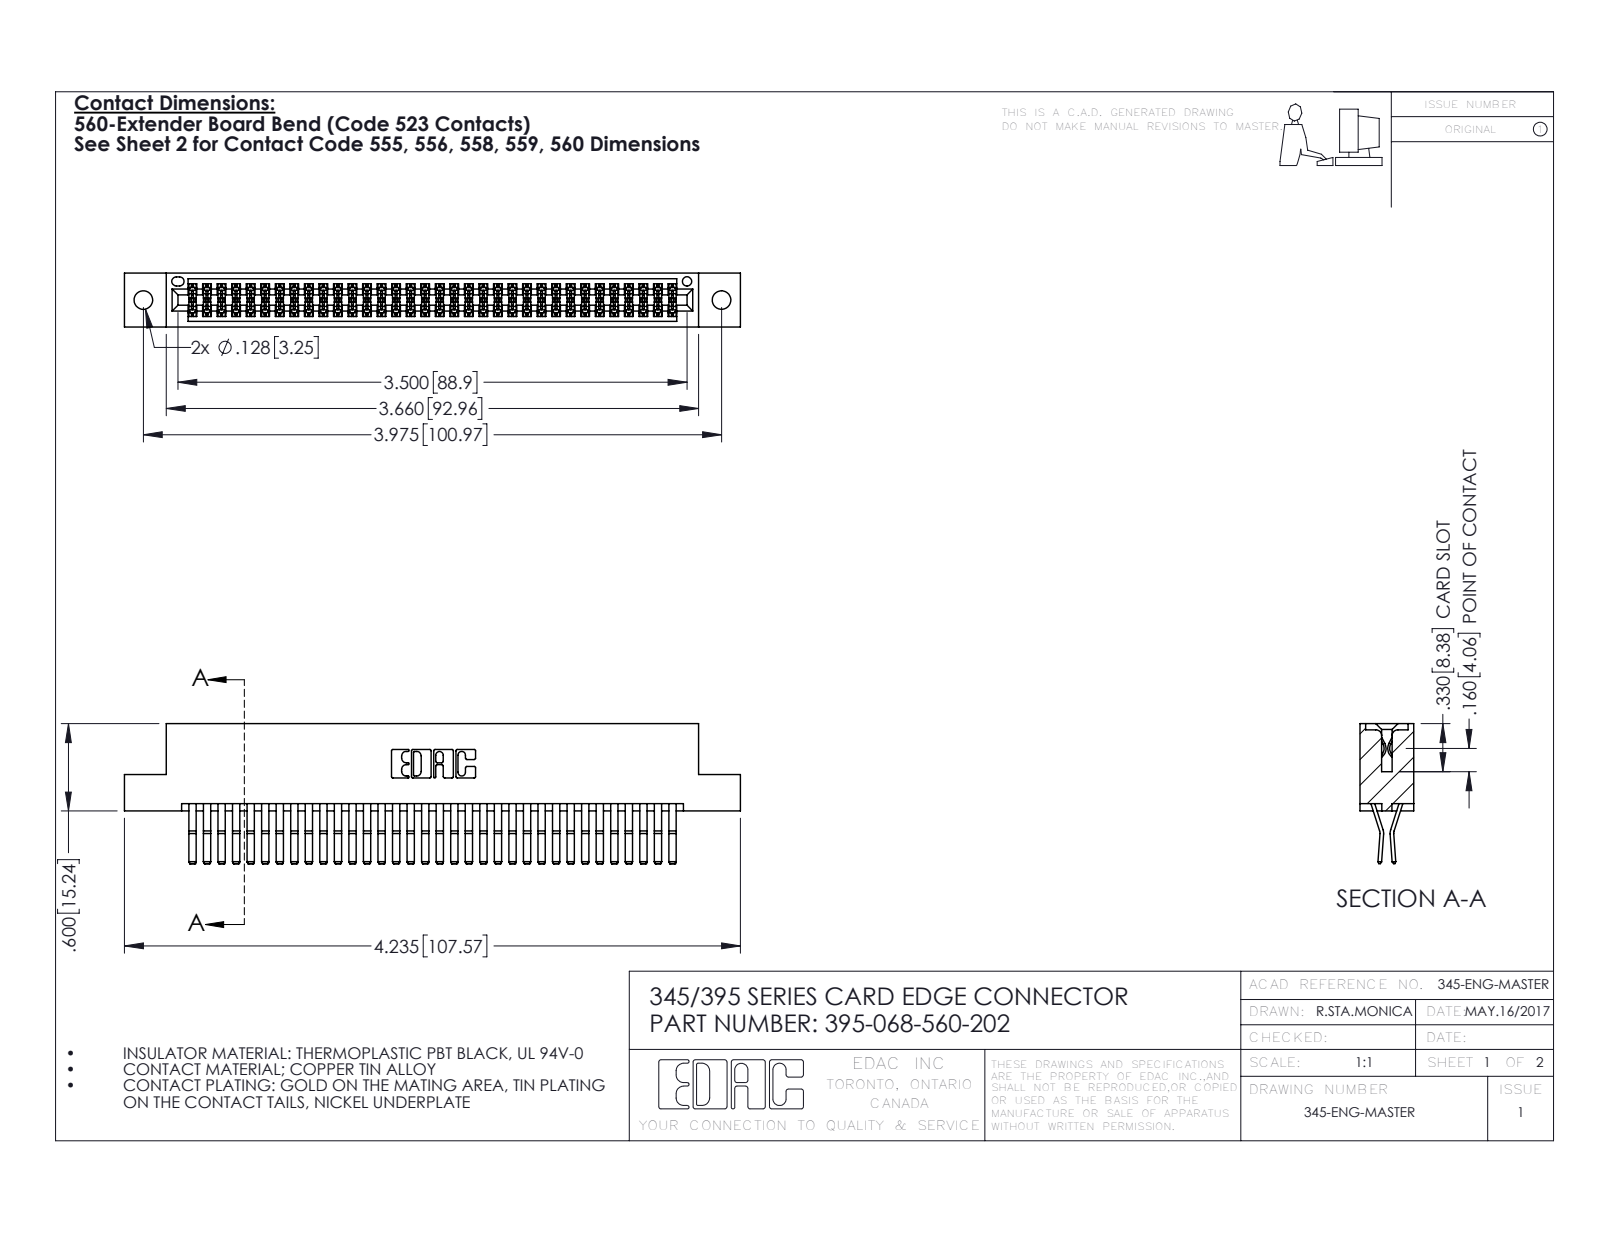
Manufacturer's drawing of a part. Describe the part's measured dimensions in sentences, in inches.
The part is named "345-292-001_560 Tail; 395-068-560-202; 345 Part_Flush Mounting Lugs - 0.128 Dia". Its 3-D file was written by "SolidWorks 2016 (CONFIG_CONTROL_DESIGN)". It is 69 solids with 3662 faces: 2324 planar, 1338 cylindrical and 0 other. Overall it measures 4.235 by 0.962 by 0.37 inches. Its volume is 0.658 cubic inches and its surface area 25.82 square inches. Round holes: 2 of diameter 0.128, 1 of diameter 0.064. Partial cylindrical surfaces (rounded edges, fillets, slot ends): 102 of radius 0.006, 22 of radius 0.01, 6 of radius 0.007, 6 of radius 0.031, 3 of radius 0.026, 2 of radius 0.01, 2 of radius 0.014, 2 of radius 0.019. The main face-to-face distances are 0.025, 0.298, 0.072, 0.2, 0.37, 0.098, 0.272, 0.225, 0.175, 0.149. The hole center spacings are 0.27, 3.74, 3.975.
